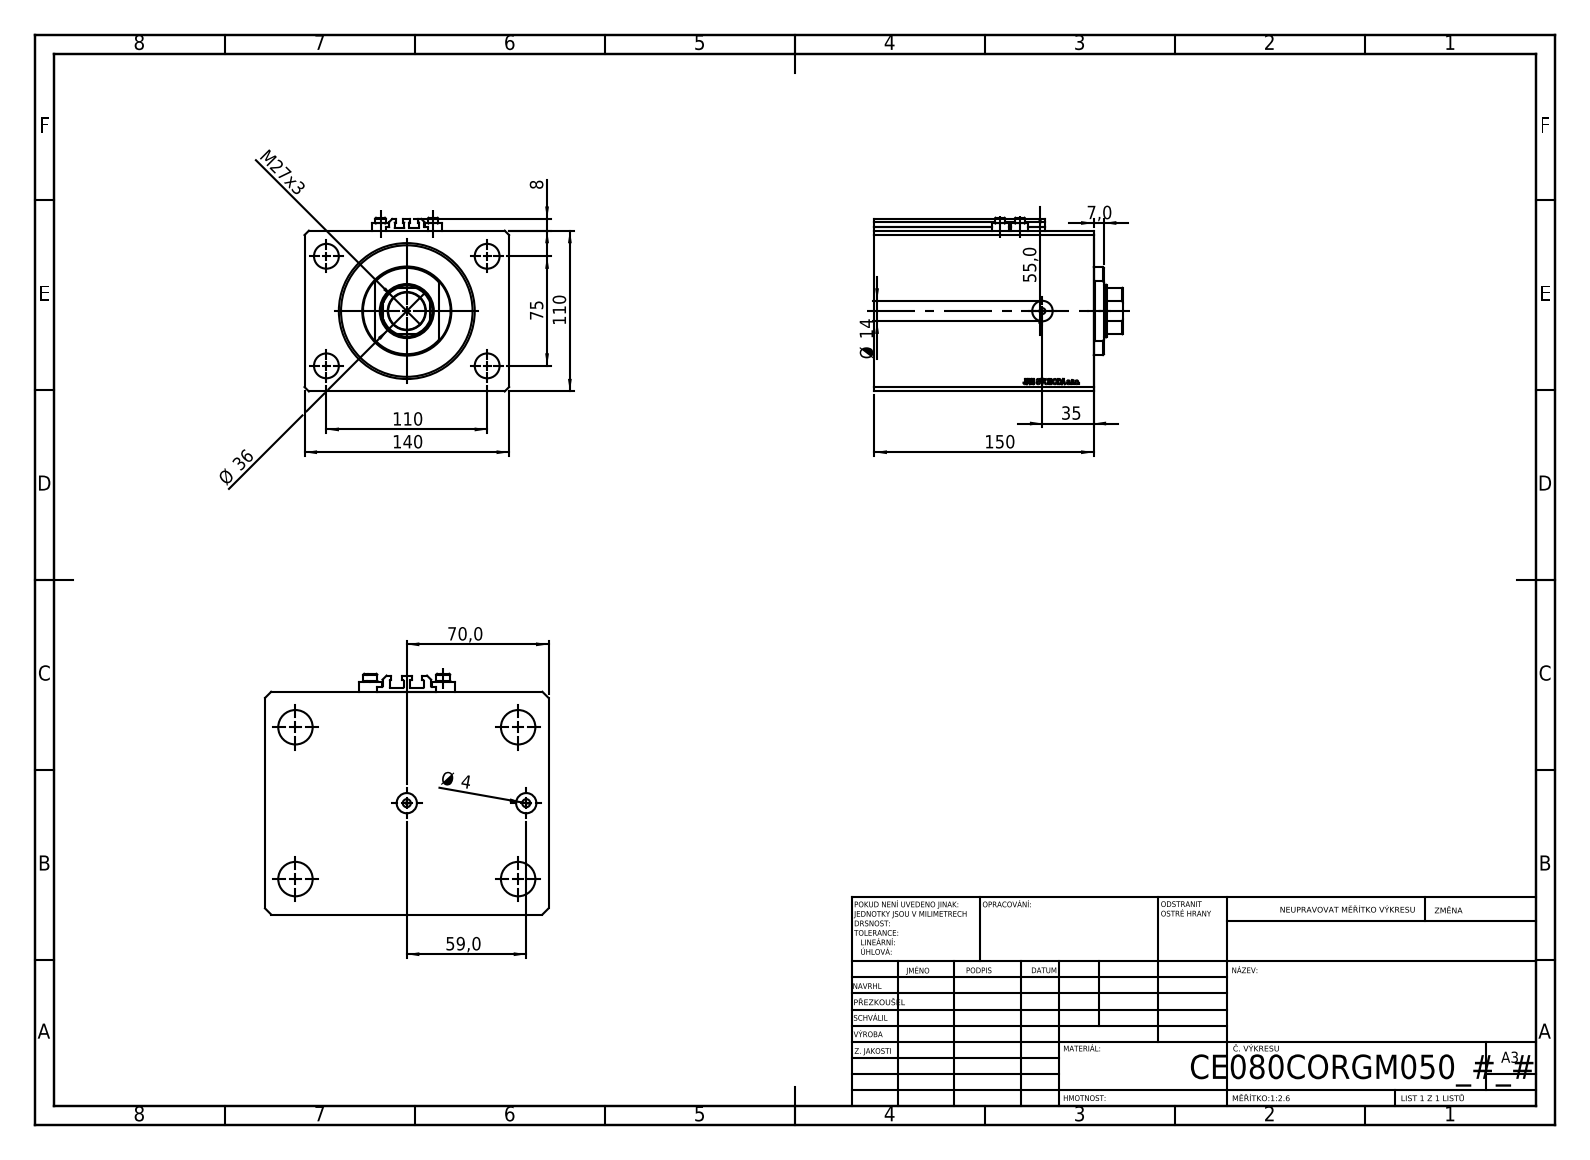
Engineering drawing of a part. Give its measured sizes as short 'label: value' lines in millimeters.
name: V250CE_C_VCP; V250CE_C_Body; V250CE_VC_C; ALLEN BOLT V250CE
written by: SolidWorks 2019 (CONFIG_CONTROL_DESIGN)
unit: mm
bodies: 8 solids, 1038 faces (504 planar, 88 cylindrical, 446 other)
size: 170 × 140 × 119
volume: 1 989 000 mm³; area: 243 302 mm²
holes: 8× ⌀4, 4× ⌀17, 2× ⌀10, 2× ⌀14, 1× ⌀1.25, 1× ⌀25.5, 1× ⌀36, 1× ⌀80, 1× ⌀93
bosses: 4× ⌀11.6, 4× ⌀7, 1× ⌀60
rounds: 10× R0.2, 1× R17.5
face distances: 110, 140, 150, 25, 125, 20, 105, 130, 80, 50
hole spacings: 66.57, 13.6, 36, 37.71, 38.48, 75, 110, 120.01
